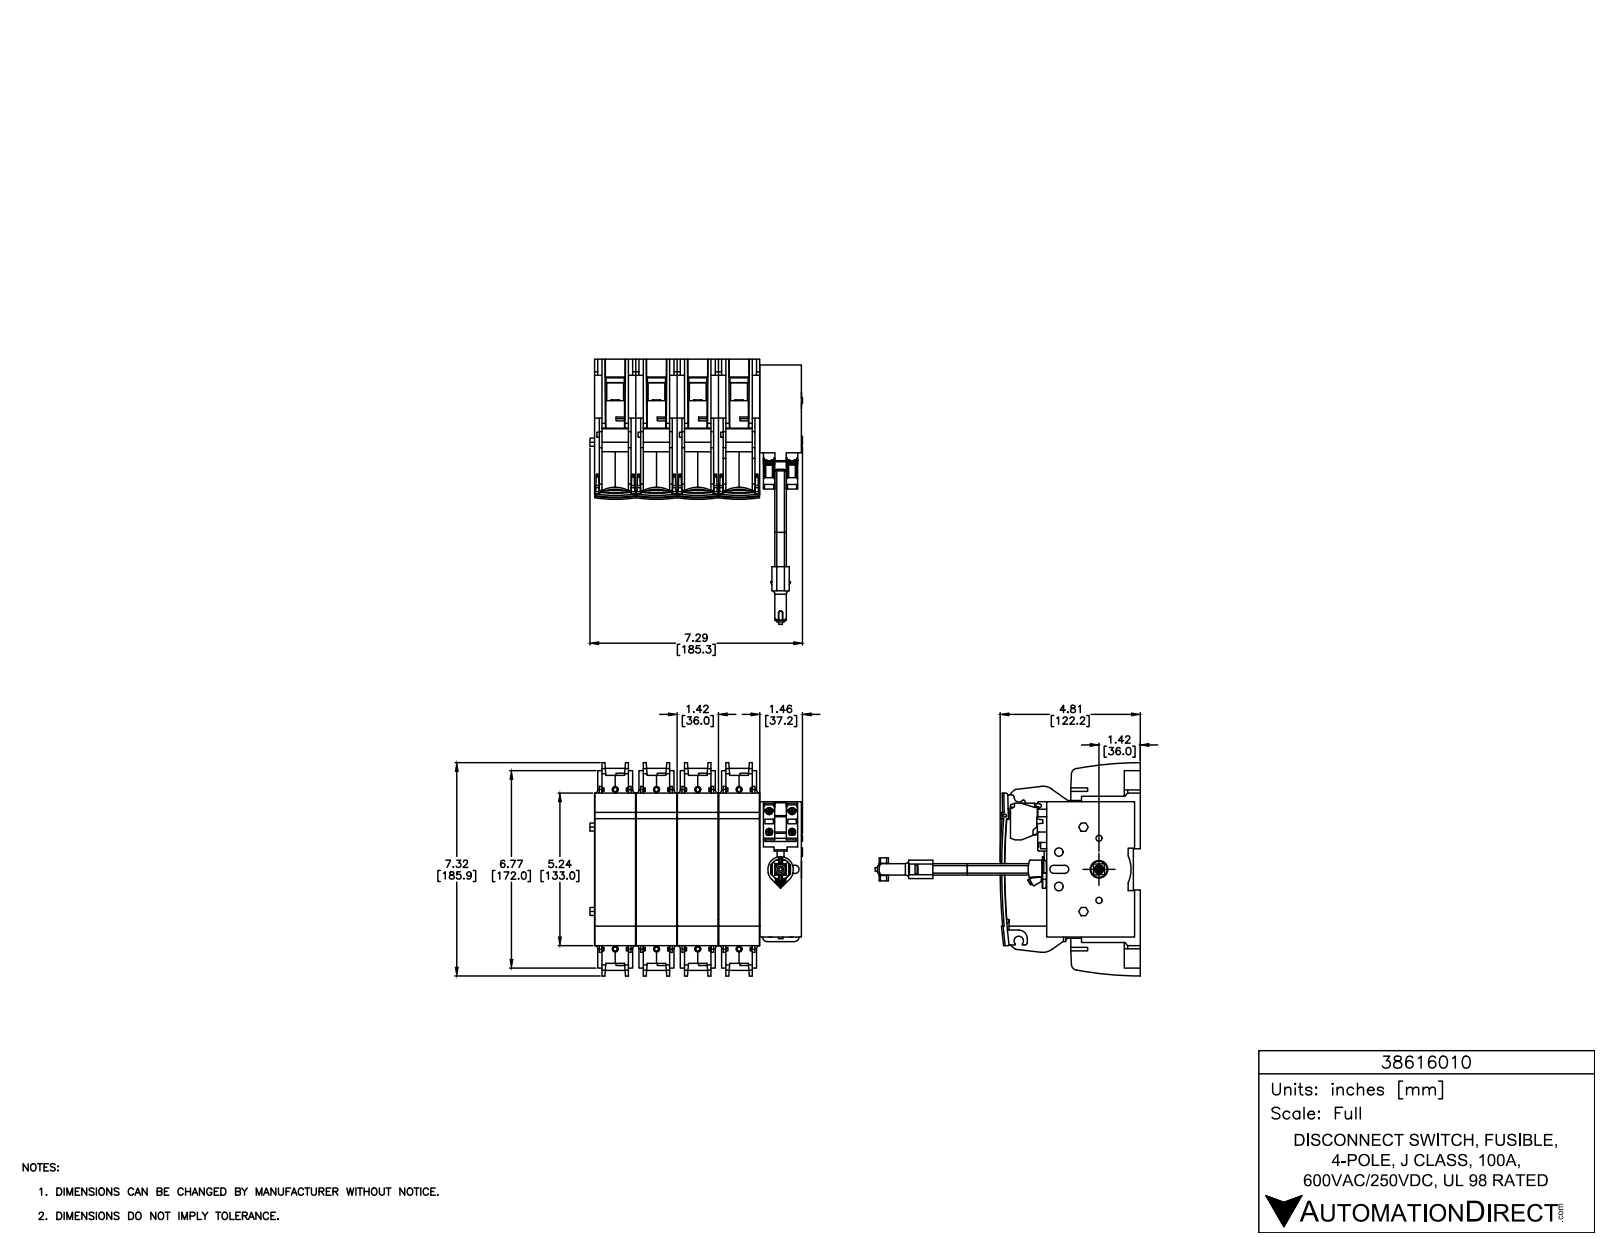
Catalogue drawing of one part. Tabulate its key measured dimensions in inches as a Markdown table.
| quantity | value |
| --- | --- |
| part name | 38616010 |
| STEP written by | SolidWorks 2015 (AUTOMOTIVE_DESIGN) |
| units | inches |
| bodies | 9 solids, 2245 faces (1256 planar, 386 cylindrical, 603 other) |
| overall size | 7.323 × 7.138 × 4.813 |
| volume | 160.6 in³ |
| surface area | 548.9 in² |
| round holes (diameter × count) | 0.205 × 8, 0.209 × 2, 0.211 × 2, 0.295 × 2, 0.098 × 1, 0.102 × 1, 0.13 × 1, 0.283 × 1, 0.602 × 1, 0.622 × 1 |
| round bosses / shafts (diameter × count) | 0.287 × 2, 0.205 × 2, 0.203 × 2, 0.63 × 1, 0.315 × 1, 0.197 × 1 |
| partial cylindrical surfaces (radius × count) | 0.106 × 32, 0.248 × 16, 0.346 × 16, 0.02 × 9, 0.043 × 8, 0.201 × 8, 0.039 × 5, 0.138 × 3 |
| main face-to-face distances | 1.417, 2.835, 4.252, 0.256, 1.161, 2.579, 1.673, 3.996, 3.091, 0.906 |
| hole center spacings | 1.417, 5.653, 2.835, 5.472, 6.163, 1.067, 1.458, 1.499 |
